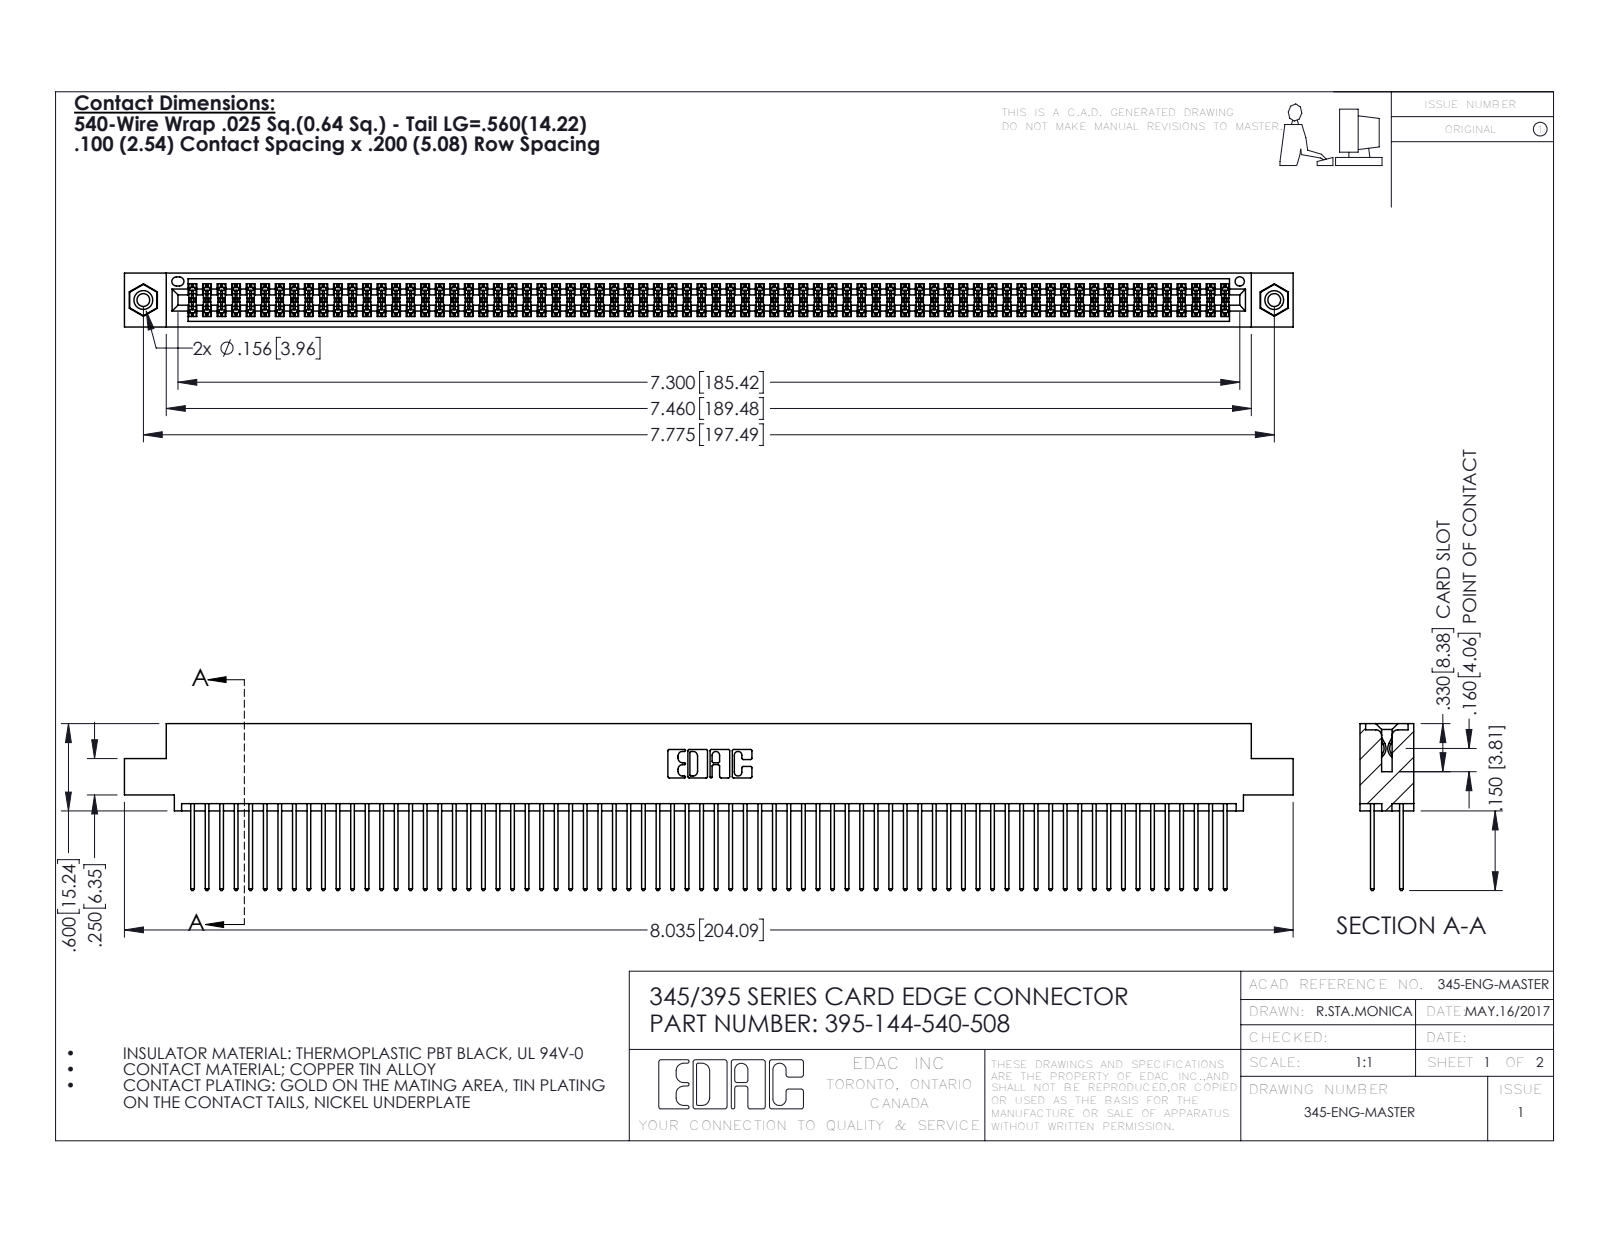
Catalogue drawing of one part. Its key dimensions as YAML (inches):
part_name: "345-292-001_345-293-140; 345-250-001_345-250-003-102; 345 Part_0.110 Offset - 0.156 Dia-TI; 395-144-540-508"
step_written_by: "SolidWorks 2016 (CONFIG_CONTROL_DESIGN)"
units: inches
bodies: {solids: 147, faces: 7390, planar: 4868, cylindrical: 2506, other: 16}
overall_size: [8.035, 1.147, 0.37]
volume: 1.255
surface_area: 52.12
round_holes:
  - {diameter: 0.089, count: 2}
  - {diameter: 0.125, count: 2}
  - {diameter: 0.156, count: 2}
  - {diameter: 0.064, count: 1}
round_bosses_or_shafts:
  - {diameter: 0.155, count: 2}
partial_cylinders:
  - {radius: 0.006, count: 216}
  - {radius: 0.01, count: 144}
  - {radius: 0.01, count: 22}
  - {radius: 0.007, count: 6}
  - {radius: 0.031, count: 6}
  - {radius: 0.026, count: 3}
  - {radius: 0.014, count: 2}
  - {radius: 0.019, count: 2}
face_to_face_distances: [0.072, 0.298, 0.2, 0.098, 0.272, 0.025, 0.225, 0.37, 0.175, 0.149]
hole_center_spacings: [0.27, 7.539, 7.775]
